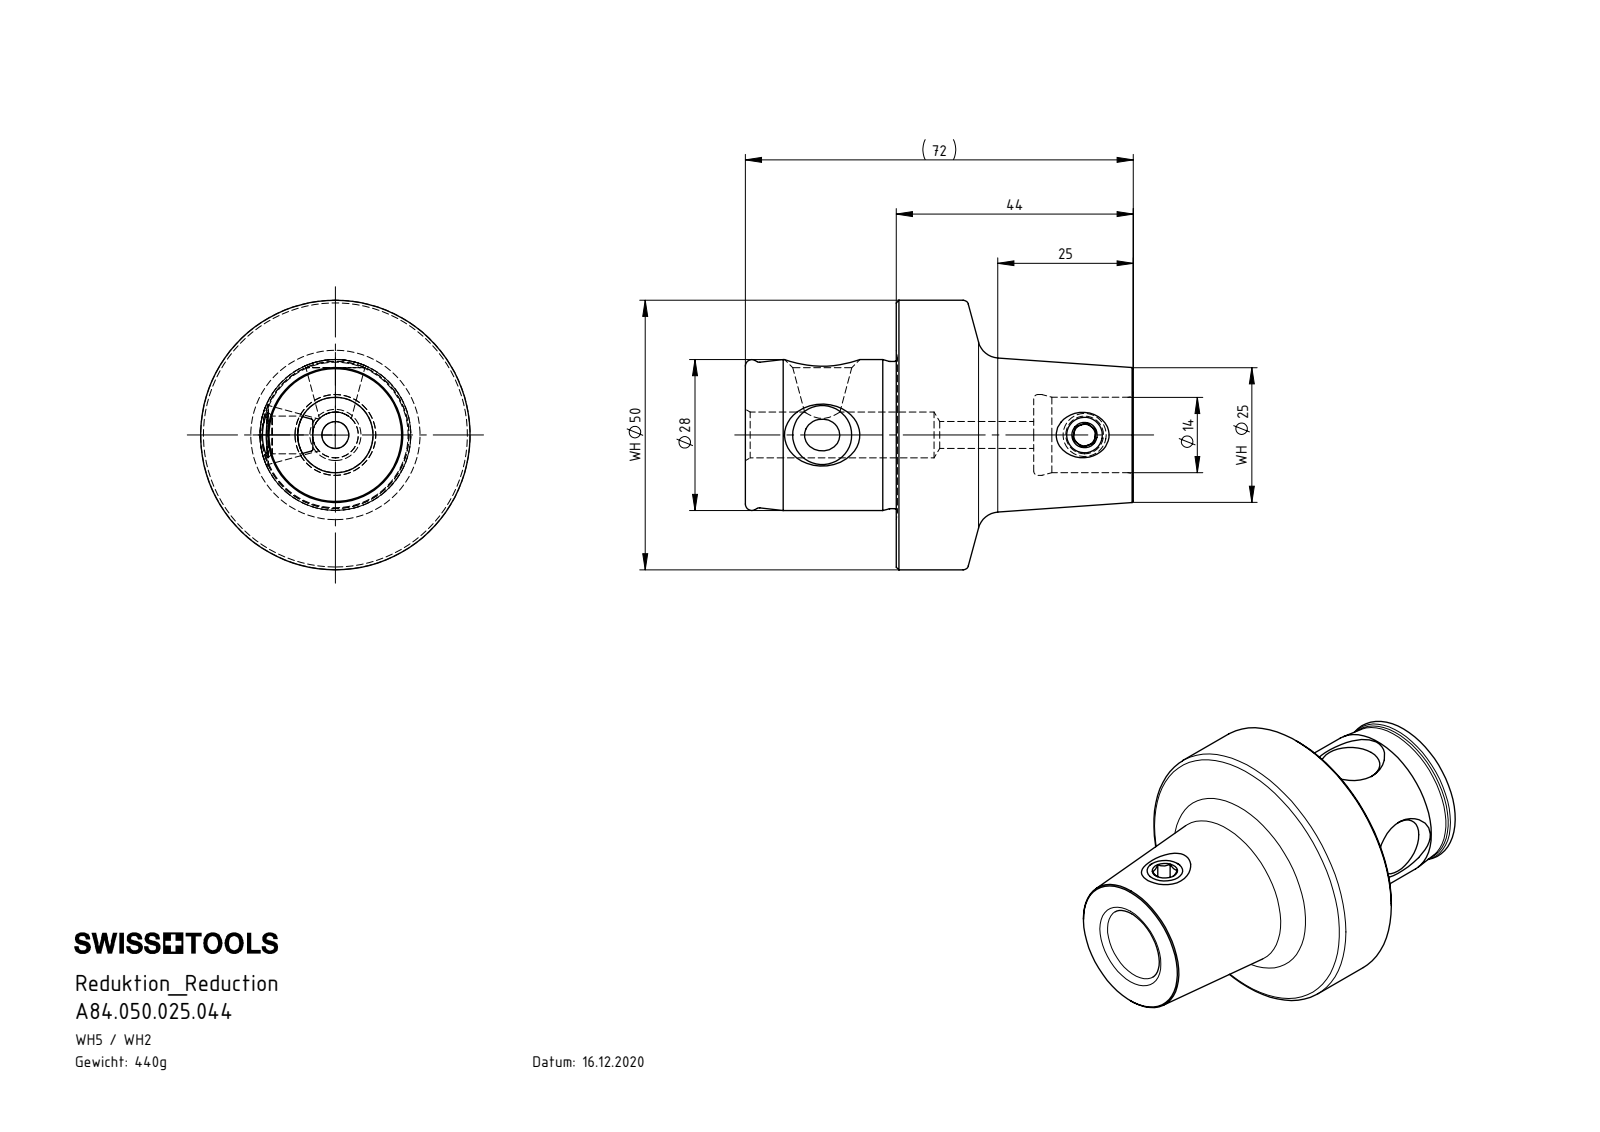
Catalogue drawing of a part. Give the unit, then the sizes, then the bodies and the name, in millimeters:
Units: millimetres
Overall size (bounding box): 72 × 50 × 50
Round holes (diameter × count): ⌀5 ×1, ⌀7 ×1, ⌀8.5 ×1, ⌀14 ×1, ⌀15 ×1
Round bosses / shafts (diameter × count): ⌀50 ×1, ⌀28 ×1, ⌀27.3 ×1, ⌀8 ×1
Main face-to-face distances: 28, 72, 44, 53.5, 25.5, 18.5, 4, 5, 10
Volume: 56 140 mm³ · Surface area: 13 218 mm²
Bodies: 2 solids, 87 faces (13 planar, 18 cylindrical, 56 other)
Part name (STEP PRODUCT): WH5-WH2.K01.044_B; A84.050.025.044; WH2-ER1.001.010
STEP written by: SolidWorks 2017 (CONFIG_CONTROL_DESIGN)
